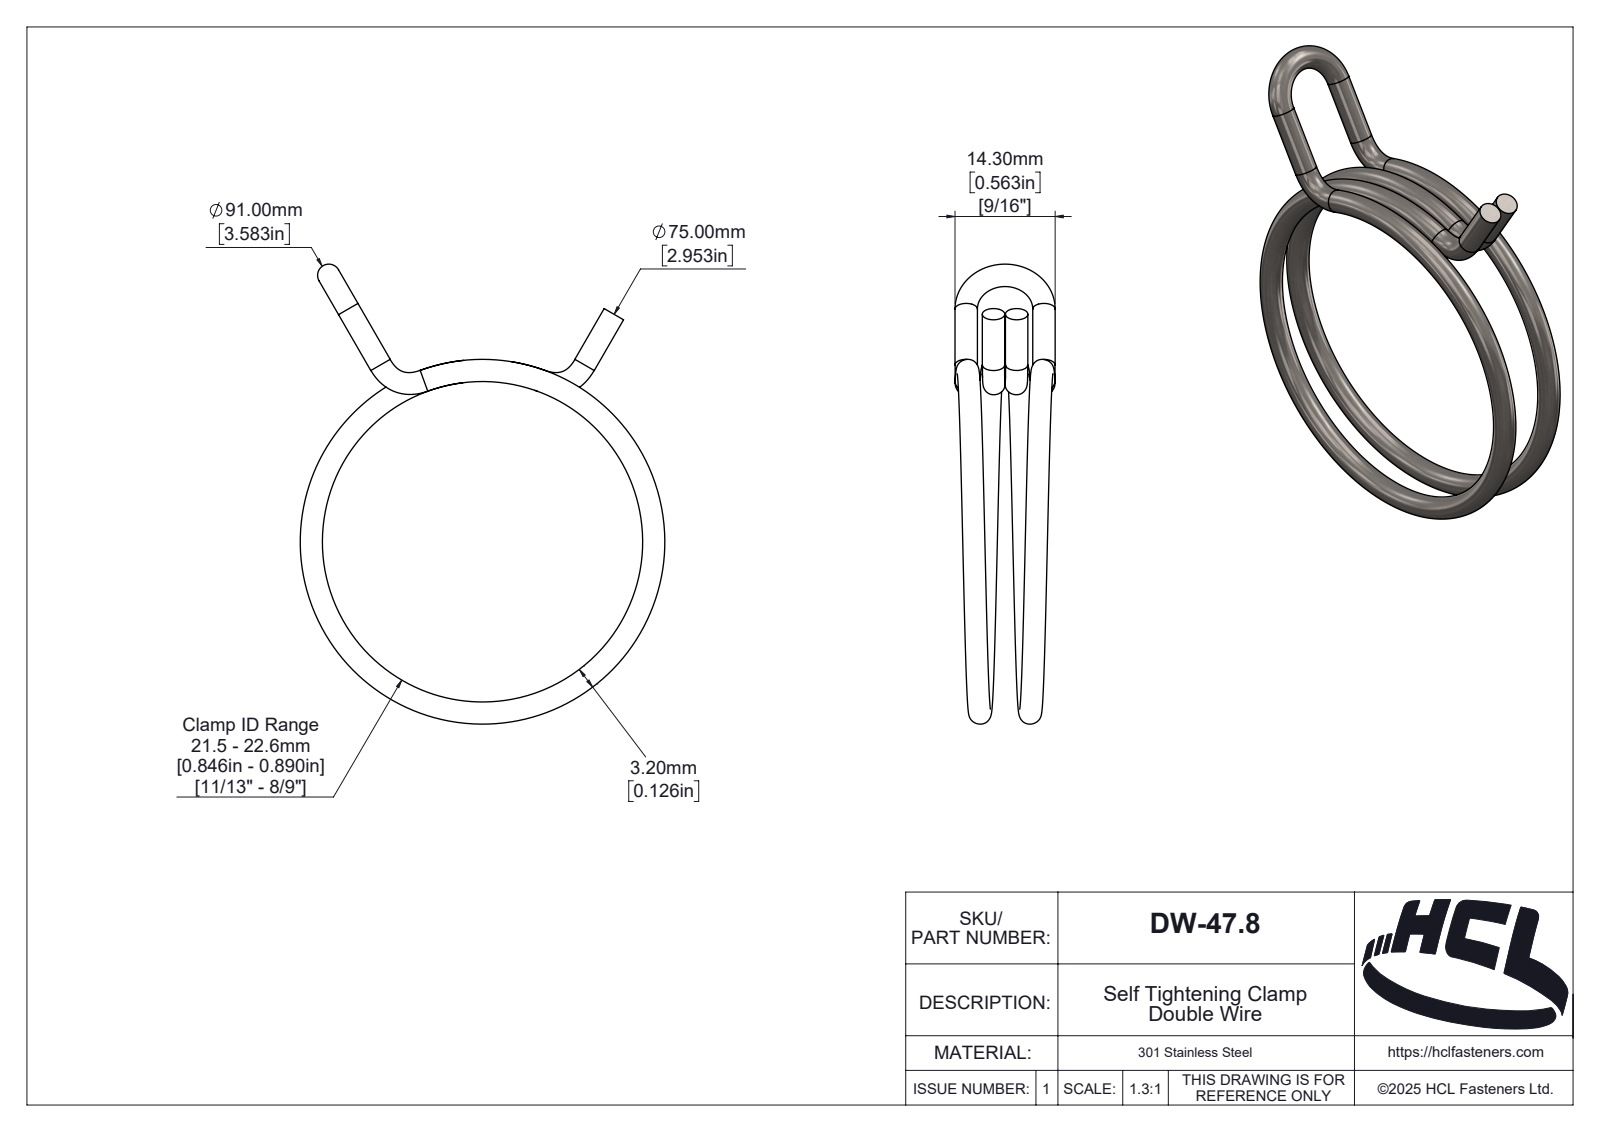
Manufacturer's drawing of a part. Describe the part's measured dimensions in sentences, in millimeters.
The part is named "DW-47.8". Its 3-D file was written by "SolidWorks 2025 (AUTOMOTIVE_DESIGN)". It is 1 solid with 132 faces: 14 planar, 53 cylindrical and 65 other. Overall it measures 65.64 by 52.06 by 14.3 millimeters. Its volume is 3 355 cubic millimeters and its surface area 4 240 square millimeters. Round bosses or shafts: 4 of diameter 3.2. Partial cylindrical surfaces (rounded edges, fillets, slot ends): 1 of radius 0.16, 1 of radius 0.2, 1 of radius 0.21, 1 of radius 0.26, 1 of radius 0.36, 1 of radius 0.48, 1 of radius 0.6, 1 of radius 0.68.
